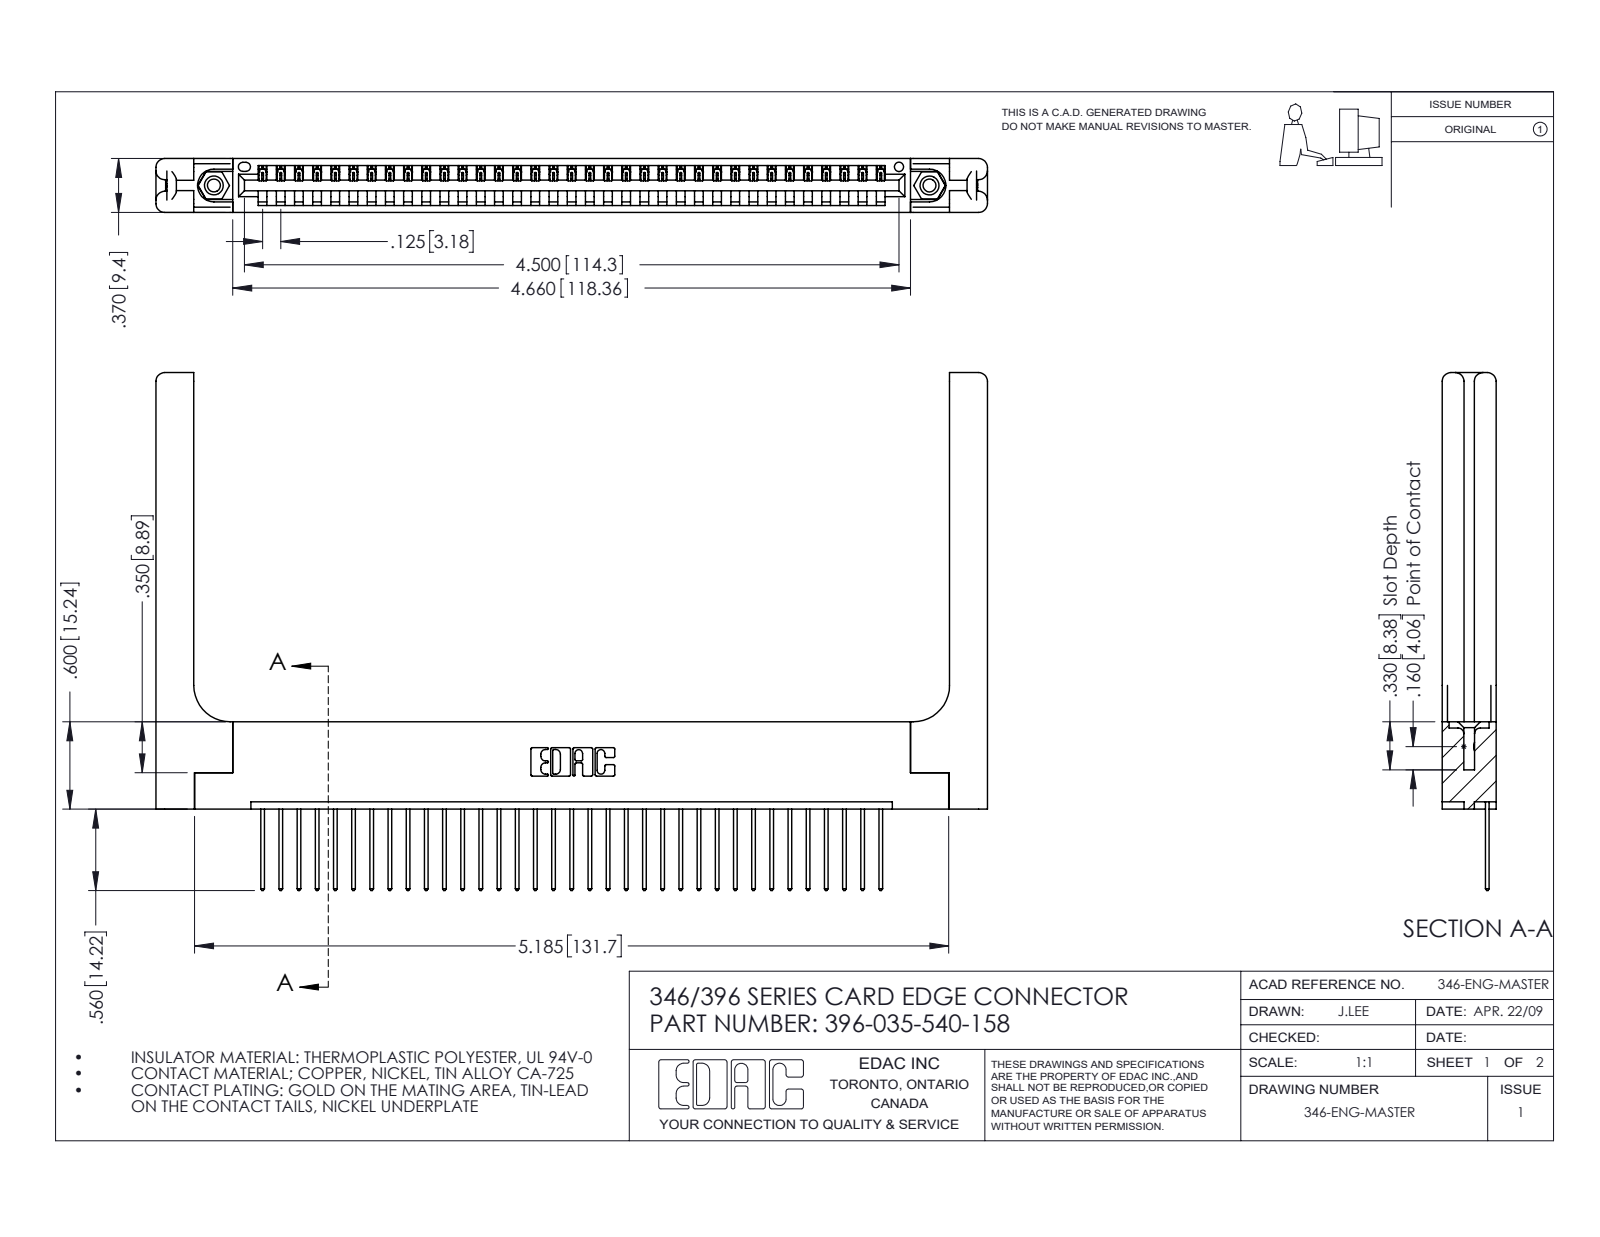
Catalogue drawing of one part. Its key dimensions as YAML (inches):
part_name: "346-220-058_345-220-058; 346 Part_Flush Mounting Lugs - 0.156 Dia-TH; 345-292-001_345-293-140; 345-250-001_345-250-001-102 (+1 more)"
step_written_by: "SolidWorks 2016 (CONFIG_CONTROL_DESIGN)"
units: inches
bodies: {solids: 40, faces: 2408, planar: 1624, cylindrical: 724, other: 60}
overall_size: [5.716, 3.56, 0.37]
volume: 1.307
surface_area: 35.35
round_holes:
  - {diameter: 0.089, count: 2}
  - {diameter: 0.125, count: 2}
  - {diameter: 0.156, count: 2}
  - {diameter: 0.064, count: 1}
round_bosses_or_shafts:
  - {diameter: 0.155, count: 2}
partial_cylinders:
  - {radius: 0.006, count: 70}
  - {radius: 0.01, count: 70}
  - {radius: 0.01, count: 22}
  - {radius: 0.06, count: 16}
  - {radius: 0.007, count: 6}
  - {radius: 0.031, count: 6}
  - {radius: 0.026, count: 3}
  - {radius: 0.03, count: 2}
face_to_face_distances: [0.37, 0.048, 0.322, 0.072, 0.148, 0.15, 0.25, 0.298, 0.025, 0.222]
hole_center_spacings: [0.246, 4.711, 4.92]
